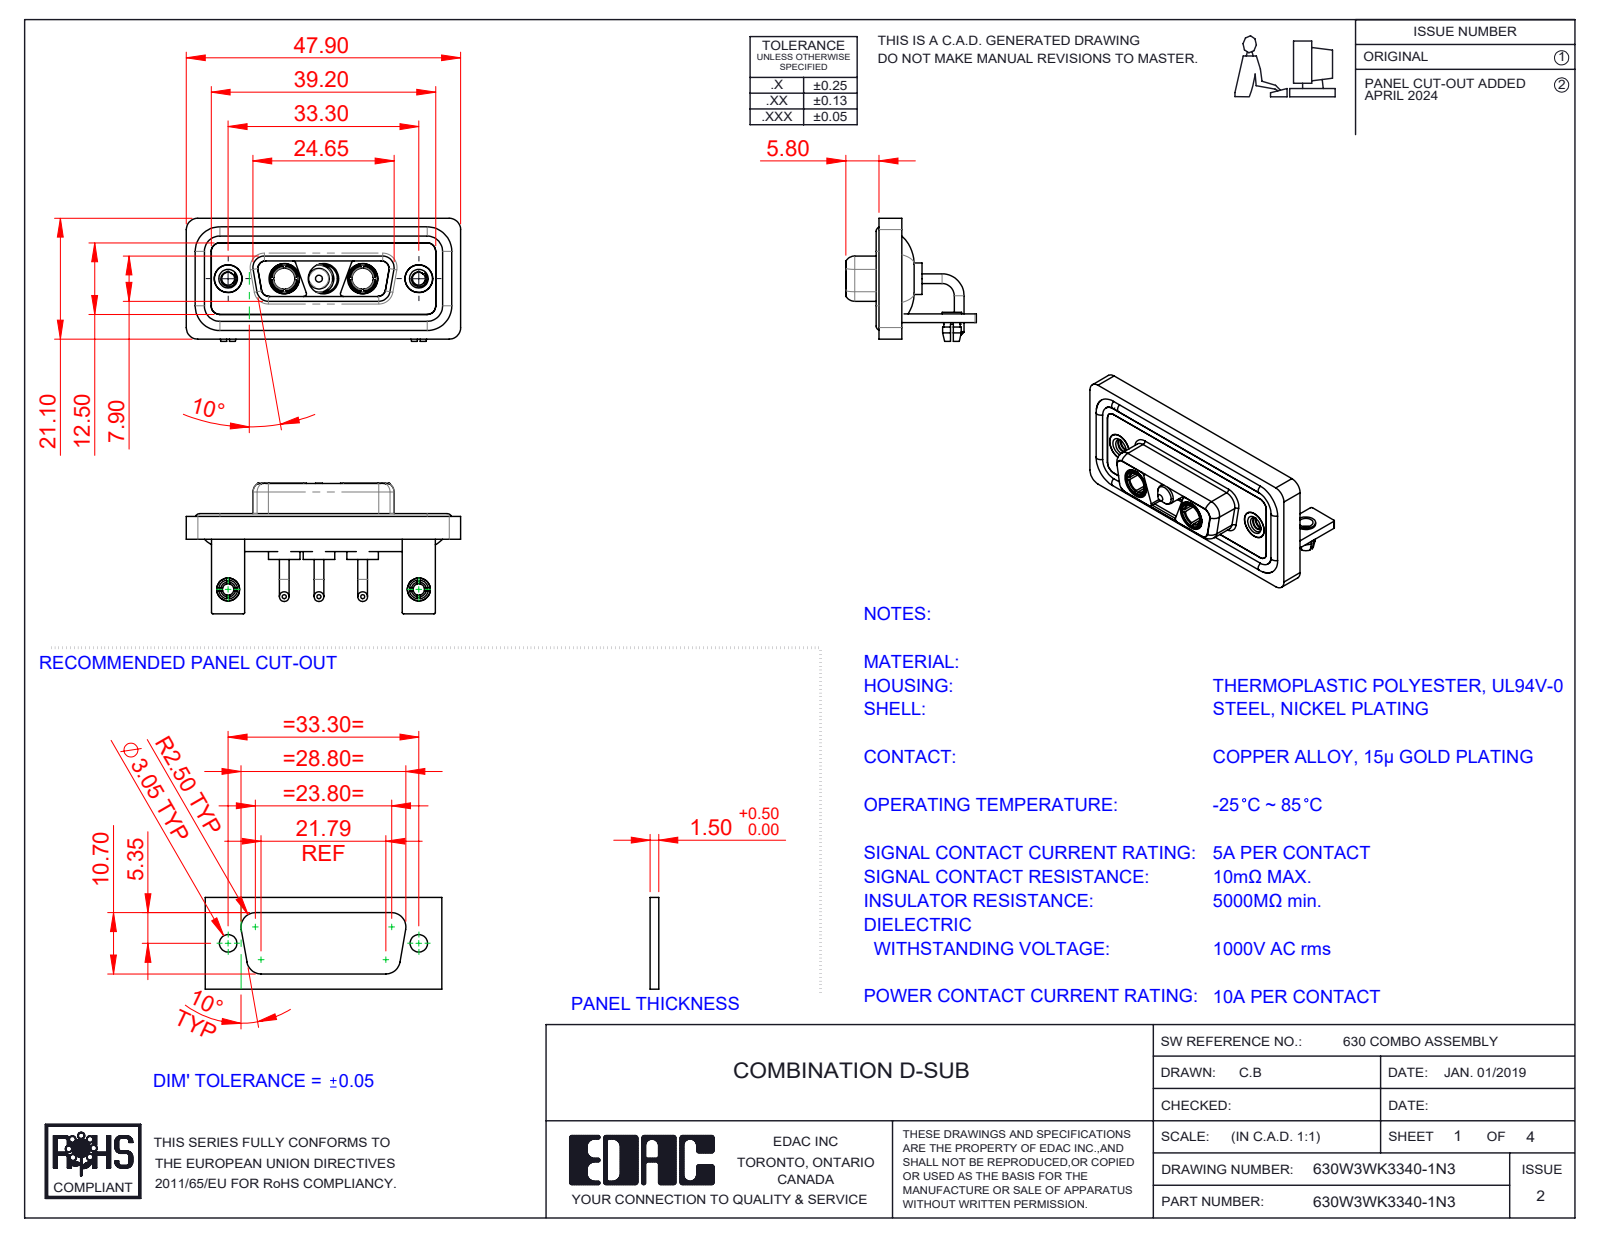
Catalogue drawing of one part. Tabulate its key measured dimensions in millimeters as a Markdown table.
| quantity | value |
| --- | --- |
| part name | 630Combo Board Lock_50 Contacts; 630Combo Housing_3WK3; Power Socket_10A RA; 630Combo Shell Rear_15 Contacts (+6 more) |
| STEP written by | SolidWorks 2023 (CONFIG_CONTROL_DESIGN) |
| units | millimeters |
| bodies | 17 solids, 735 faces (246 planar, 320 cylindrical, 169 other) |
| overall size | 47.9 × 22.8 × 21.5 |
| volume | 6 261 mm³ |
| surface area | 10 532 mm² |
| round holes (diameter × count) | 4.85 × 5, 5.3 × 3, 2 × 2, 2.26 × 2, 2.5 × 2, 3.2 × 2, 3.7 × 2, 4 × 2, 4.05 × 2, 5 × 2 |
| round bosses / shafts (diameter × count) | 1.7 × 6, 1.6 × 4, 5.5 × 3, 5.2 × 3, 4.75 × 3, 3.75 × 3, 4.96 × 2, 4.95 × 2 |
| partial cylindrical surfaces (radius × count) | 2 × 21, 1.5 × 18, 0.25 × 16, 1.35 × 12, 0.5 × 9, 1.6 × 8, 0.6 × 4, 0.65 × 4 |
| main face-to-face distances | 0.4, 2.9, 1.5, 3.7, 1.8, 1.1, 4.1, 1.6, 2.5, 1.4 |
| hole center spacings | 6.85, 9.8, 16.65, 23.5, 33.3, 13.7 |
